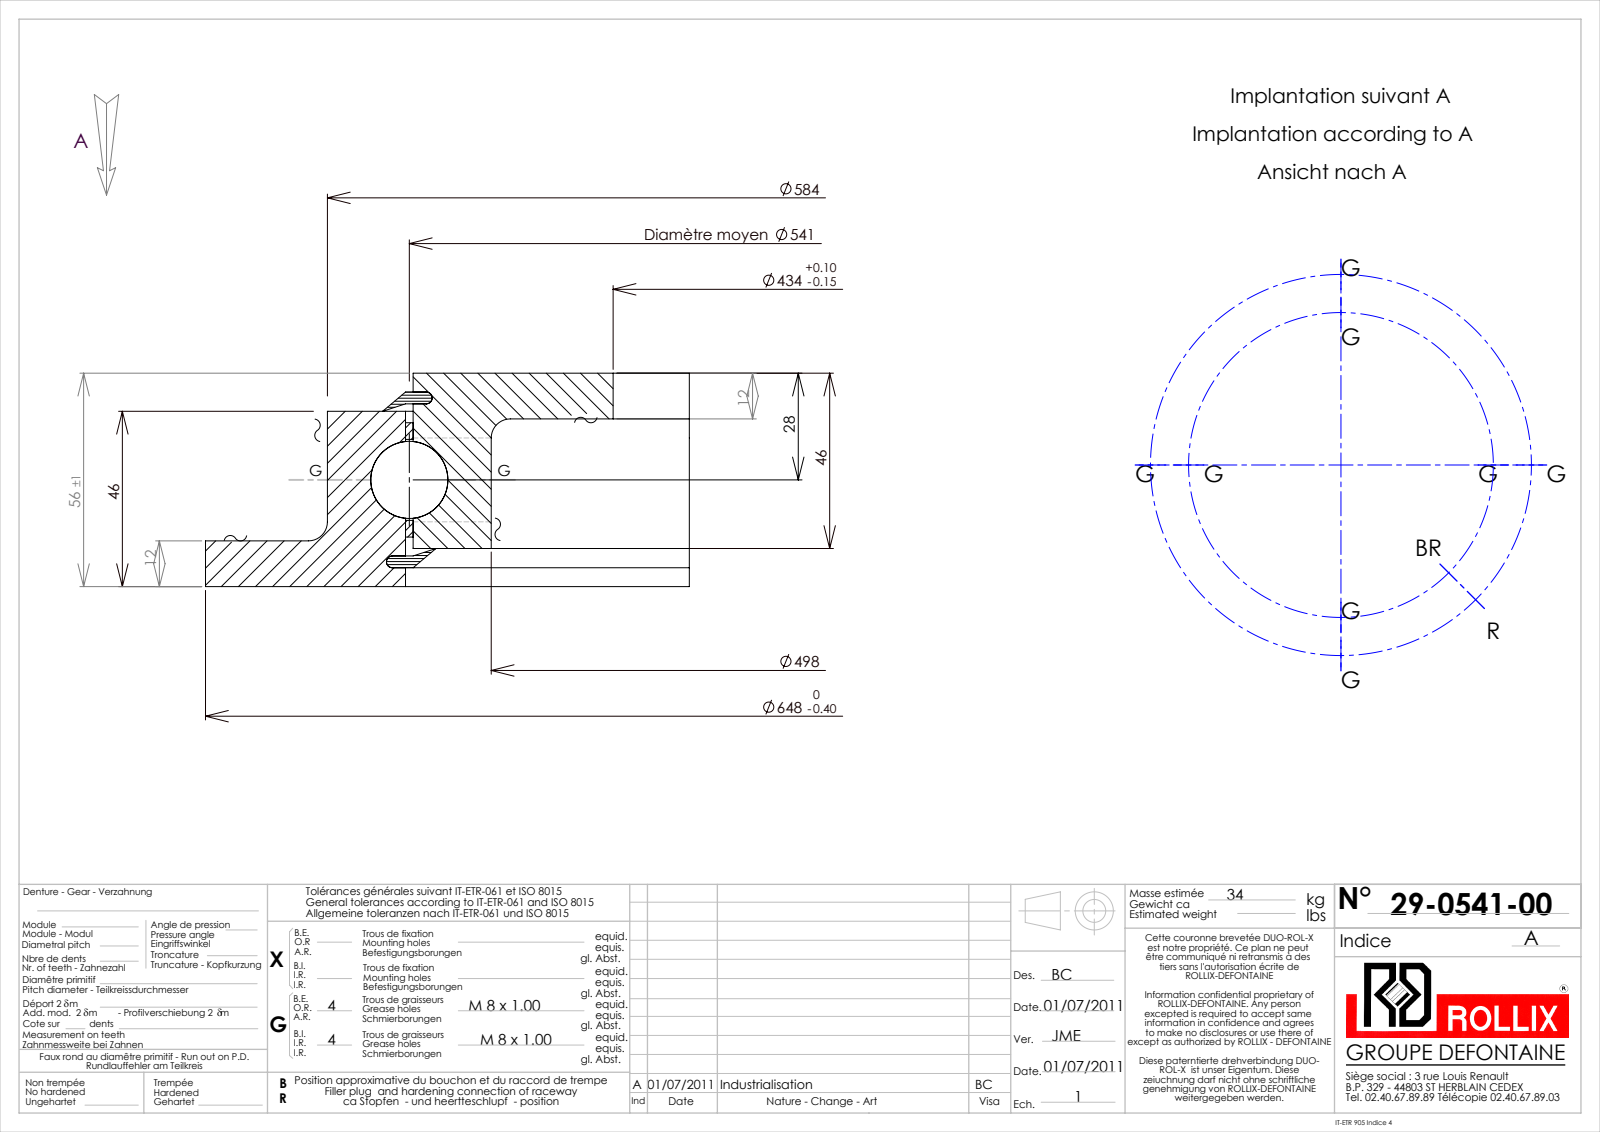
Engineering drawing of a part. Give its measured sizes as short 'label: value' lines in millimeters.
name: 23-0541-00
written by: SolidWorks 2016 (CONFIG_CONTROL_DESIGN)
unit: mm
bodies: 13 solids, 258 faces (94 planar, 52 cylindrical, 112 other)
size: 648 × 648 × 56
volume: 4 032 000 mm³; area: 815 630 mm²
holes: 8× ⌀7, 1× ⌀434, 1× ⌀498, 1× ⌀545.5
bosses: 8× ⌀8, 1× ⌀648, 1× ⌀584, 1× ⌀536.5
face distances: 12, 44, 56, 10, 46, 2, 34, 32, 36, 8.05
hole spacings: 0.4
